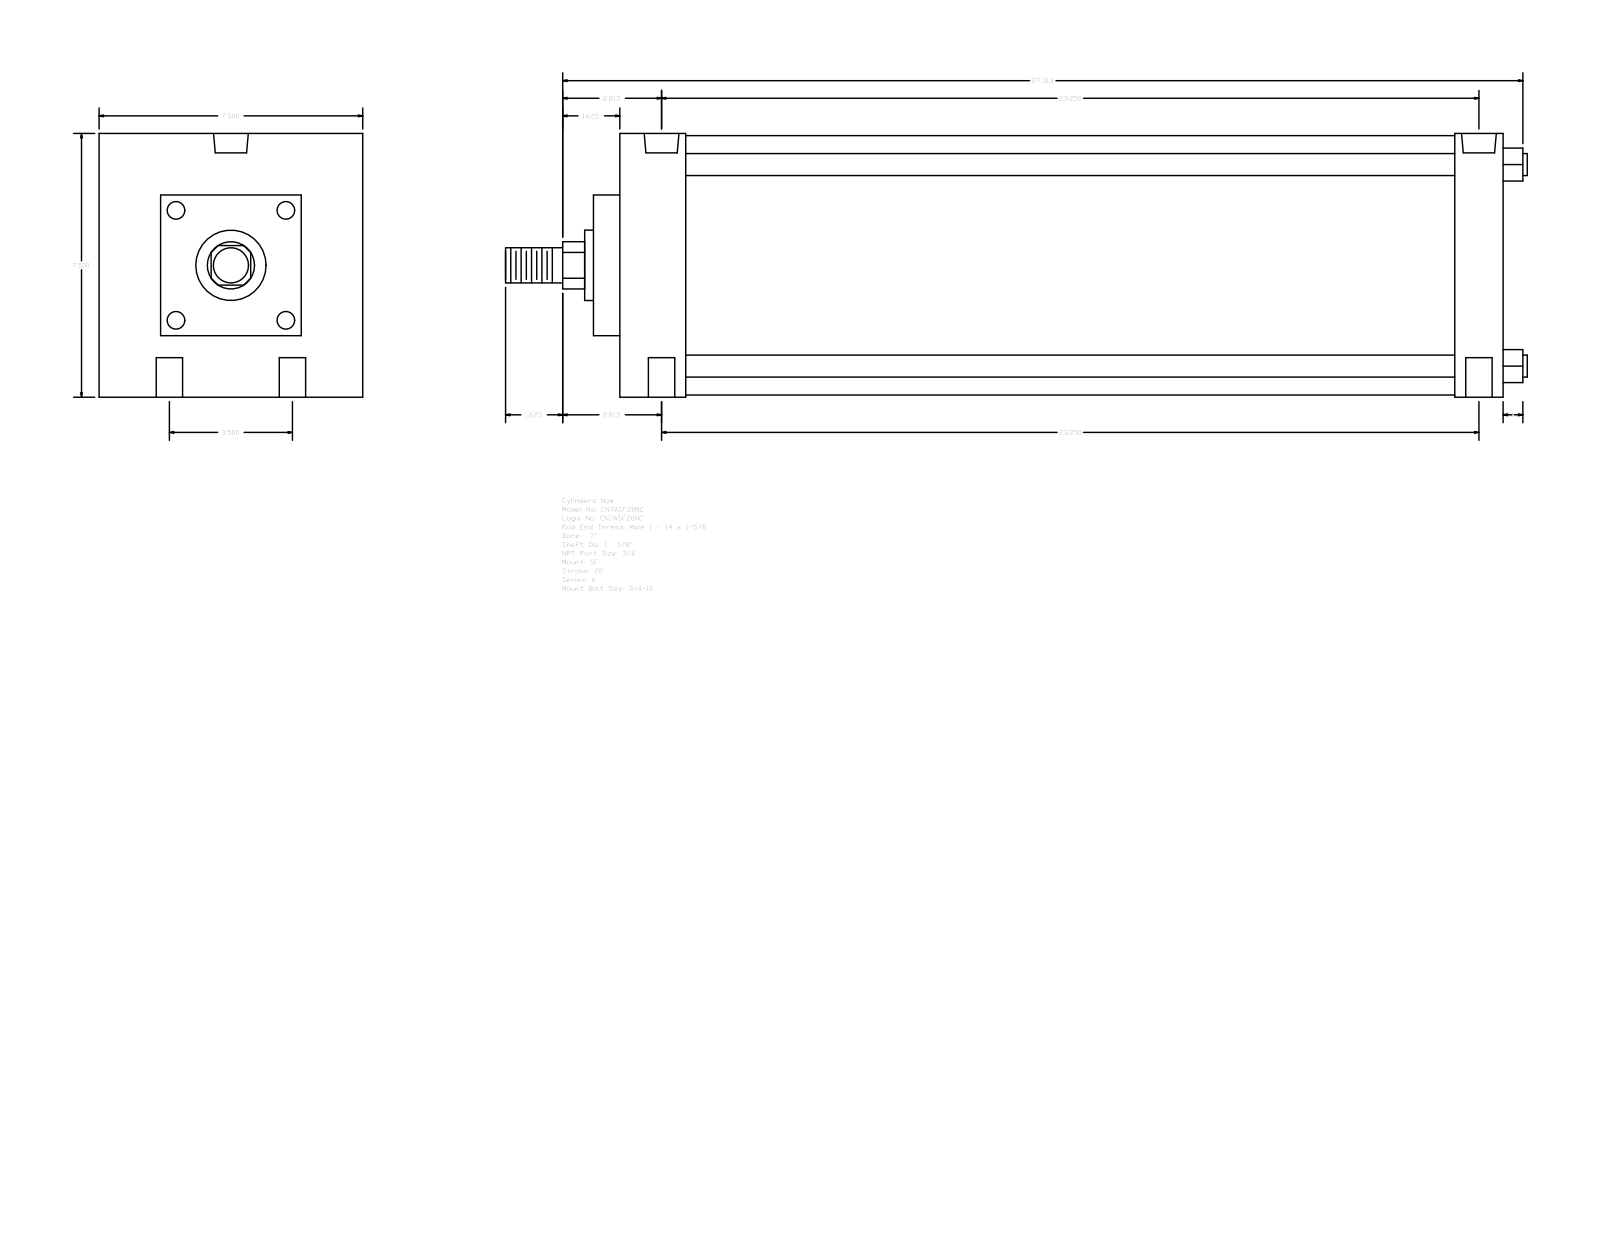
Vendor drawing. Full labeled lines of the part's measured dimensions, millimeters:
Part name (STEP PRODUCT): A_SF__0700_1.375
STEP written by: GSSL Pune (CONFIG_CONTROL_DESIGN)
Units: millimetres
Bodies: 0 solids, 93 faces (67 planar, 26 cylindrical, 0 other)
Overall size (bounding box): 738.19 × 190.5 × 190.5
Round holes (diameter × count): ⌀19.05 ×4, ⌀15.08 ×2, ⌀25.12 ×2
Round bosses / shafts (diameter × count): ⌀15.88 ×4, ⌀187.32 ×1, ⌀50.8 ×1, ⌀34.92 ×1, ⌀25.4 ×1
Partial cylindrical surfaces — rounded edges, fillets, slot ends (radius × count): R17.06 ×1
Main face-to-face distances: 190.5, 638.18, 19.04, 657.22, 66.67, 622.29, 47.63, 603.25, 555.62, 590.55
Hole centre spacings: 44.45, 592.22, 590.55, 88.9, 597.2, 579.43
